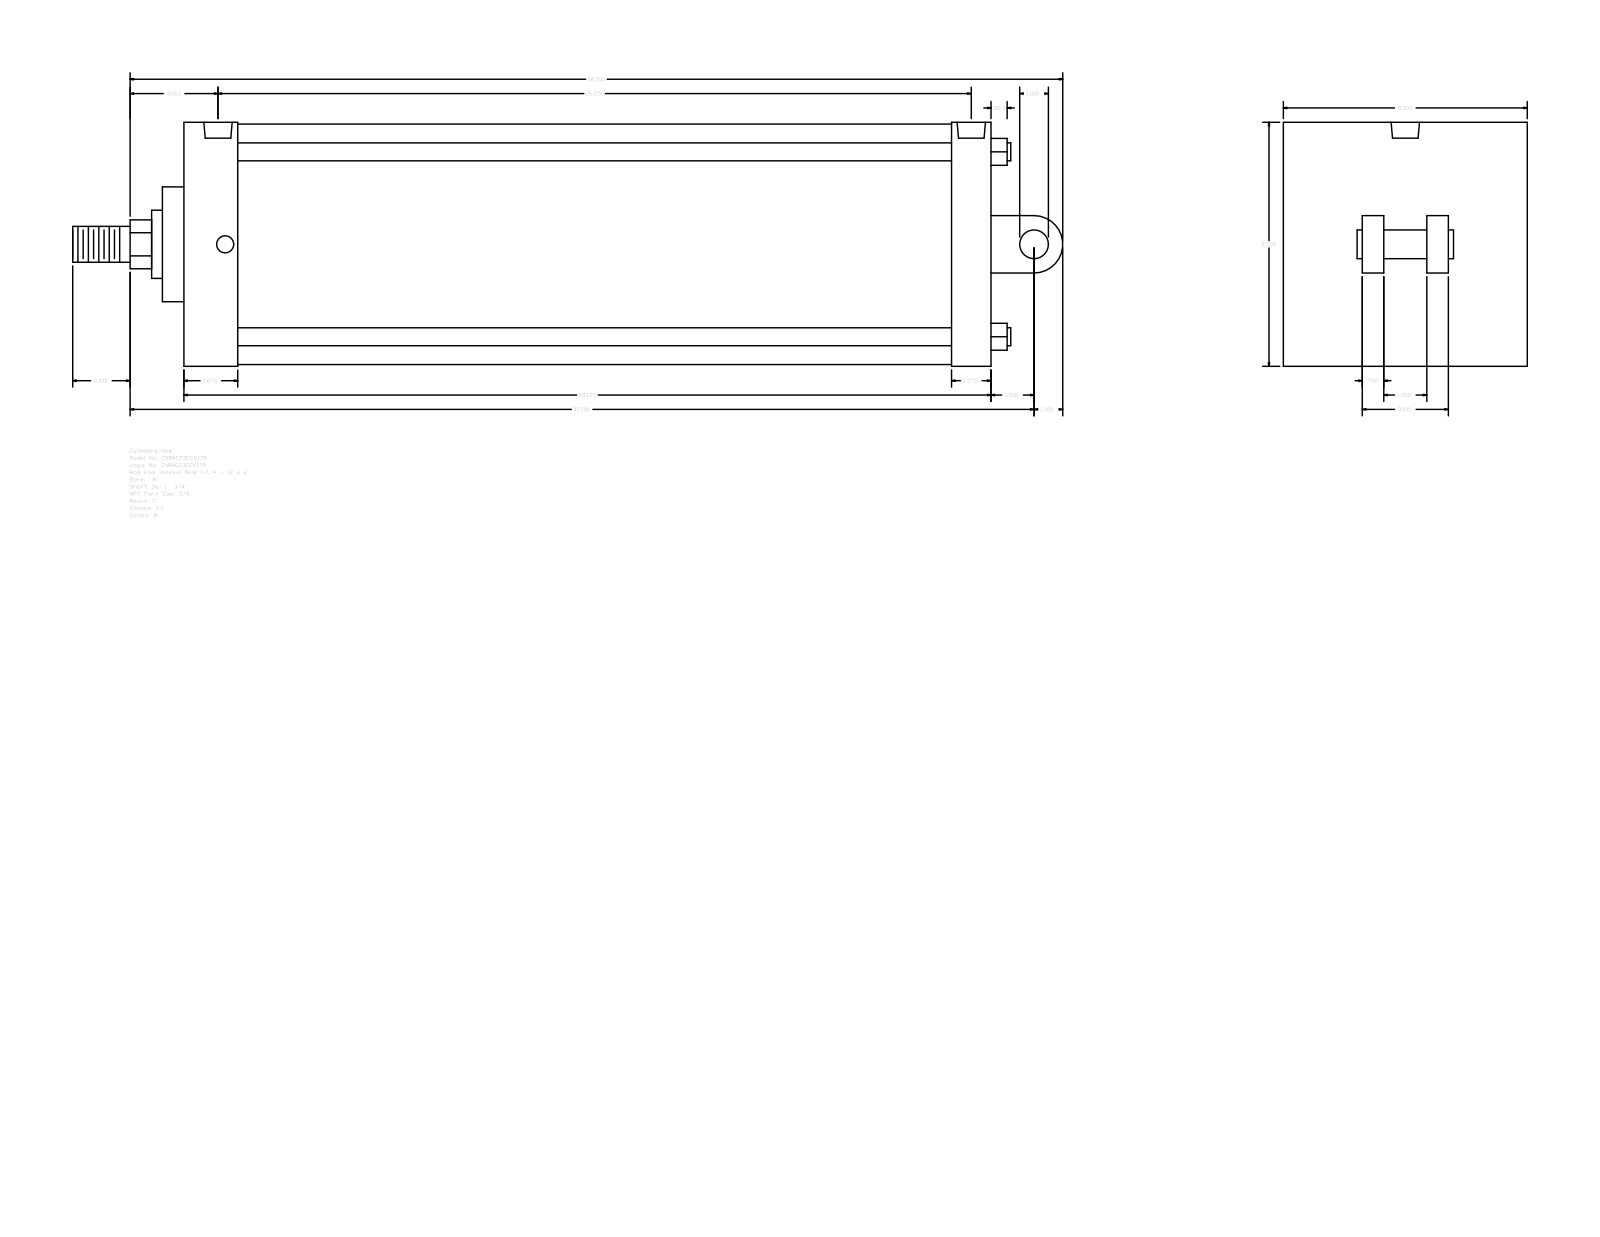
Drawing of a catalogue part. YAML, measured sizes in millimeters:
part_name: "A_C__0800_1.75"
step_written_by: "GSSL Pune (CONFIG_CONTROL_DESIGN)"
units: millimeters
bodies: {solids: 0, faces: 104, planar: 75, cylindrical: 29, other: 0}
overall_size: [876.3, 215.9, 215.9]
round_holes:
  - {diameter: 15.08, count: 4}
  - {diameter: 25.12, count: 2}
round_bosses_or_shafts:
  - {diameter: 15.88, count: 4}
  - {diameter: 212.72, count: 1}
  - {diameter: 60.33, count: 1}
  - {diameter: 44.45, count: 1}
  - {diameter: 31.75, count: 1}
  - {diameter: 25.4, count: 1}
partial_cylinders:
  - {radius: 21.63, count: 1}
  - {radius: 25.4, count: 1}
face_to_face_distances: [714.38, 215.9, 19.05, 57.15, 47.63, 666.75, 679.46, 631.83, 34.92, 69.85]
hole_center_spacings: [6.35, 654.05, 660.4, 666.75]
